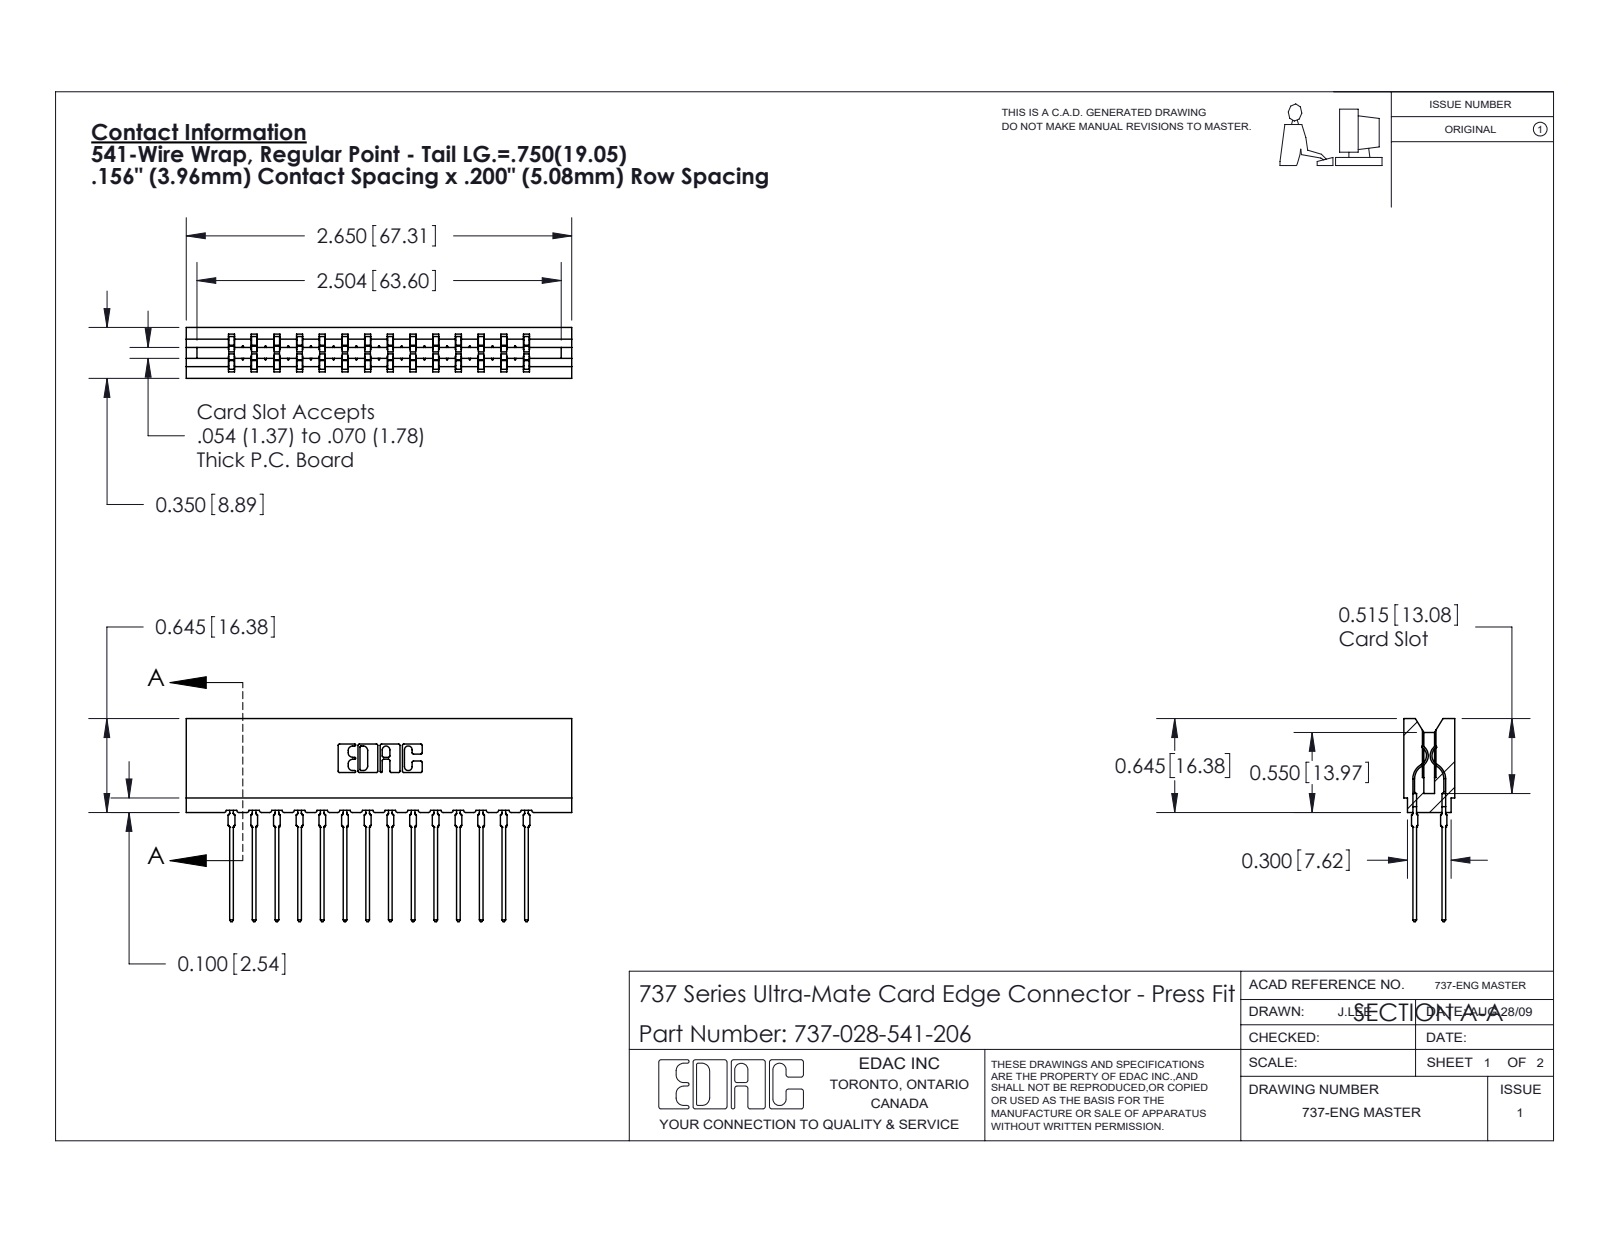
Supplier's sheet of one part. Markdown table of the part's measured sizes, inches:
| quantity | value |
| --- | --- |
| part name | 737-028-541-206; 737 Part_Insulator Option - 06; 745-292-001_541 |
| STEP written by | SolidWorks 2020 (CONFIG_CONTROL_DESIGN) |
| units | inches |
| bodies | 29 solids, 2615 faces (1357 planar, 530 cylindrical, 728 other) |
| overall size | 2.65 × 1.396 × 0.35 |
| volume | 0.424 in³ |
| surface area | 15.68 in² |
| partial cylindrical surfaces (radius × count) | 0.021 × 56, 0.015 × 28, 0.01 × 22, 0.005 × 8, 0.011 × 8, 0.007 × 6, 0.031 × 6, 0.026 × 3 |
| main face-to-face distances | 0.138, 0.212, 0.35, 0.156, 0.624, 0.063, 0.287, 0.076, 0.149, 0.78 |
